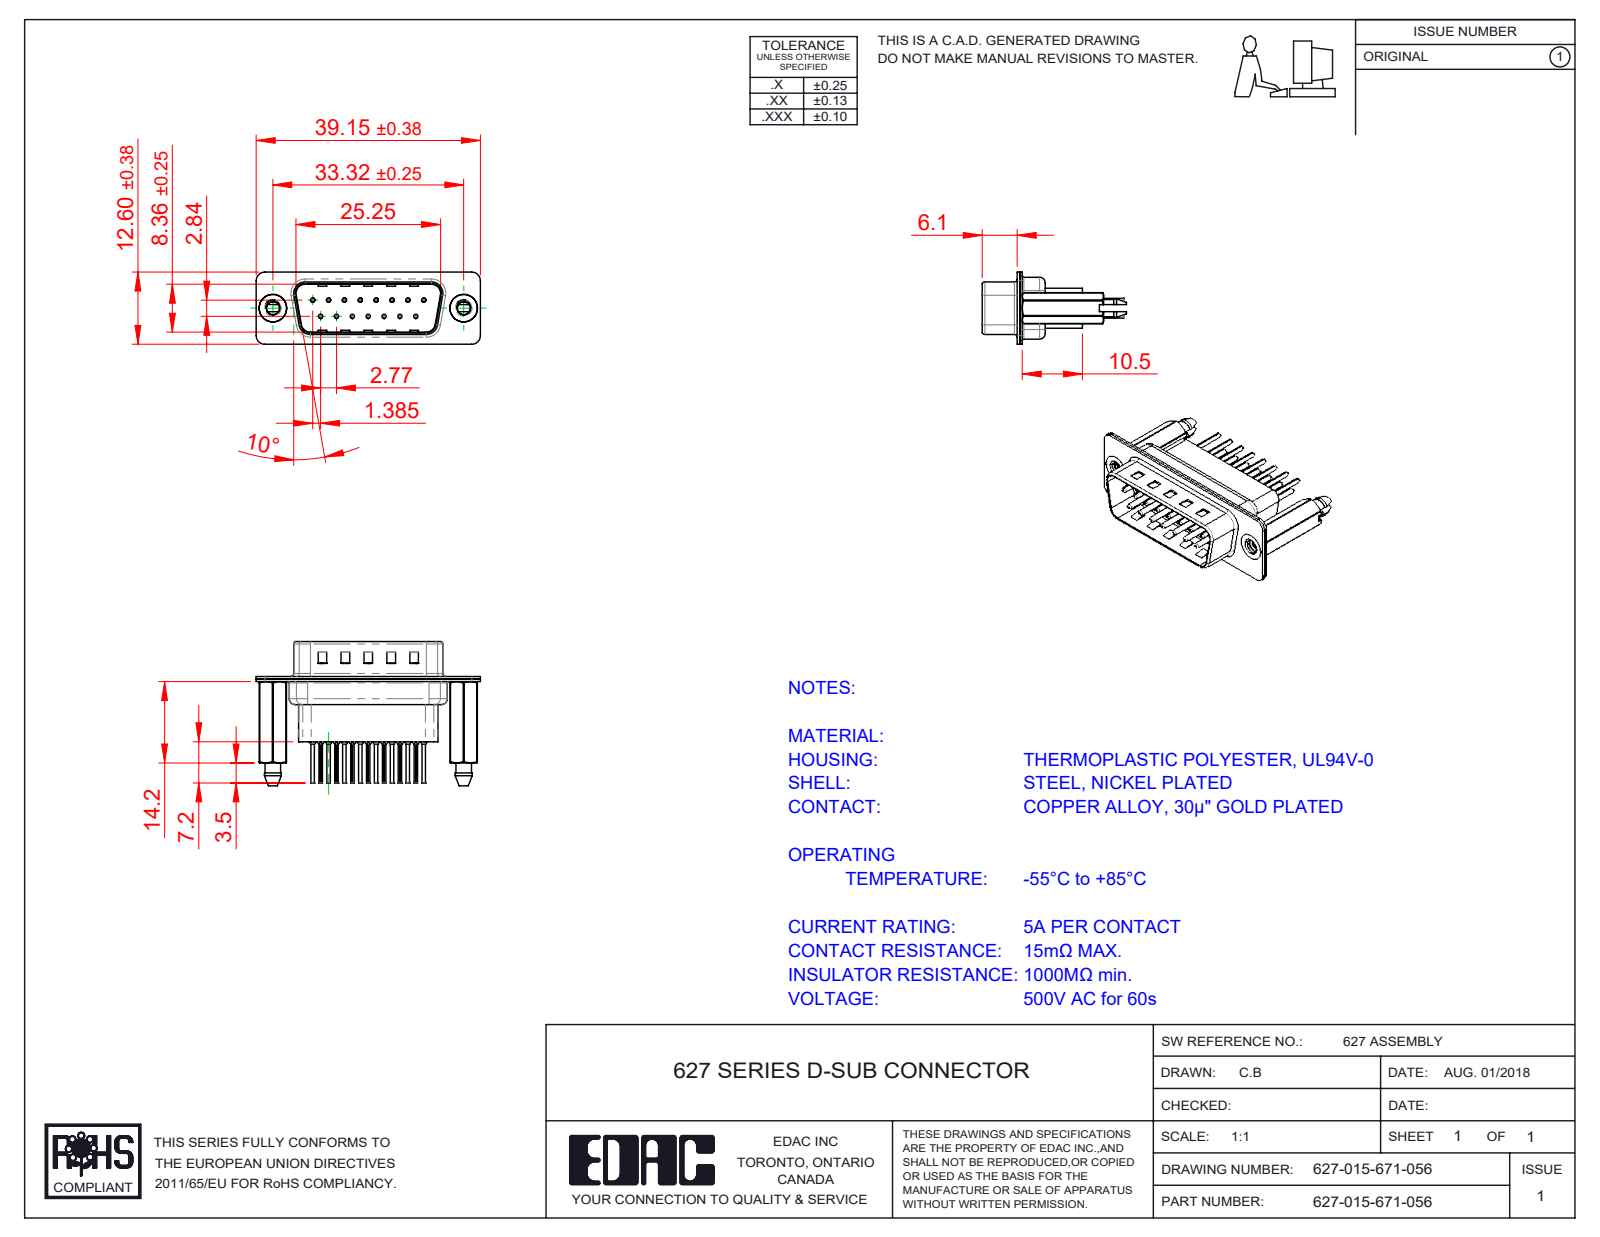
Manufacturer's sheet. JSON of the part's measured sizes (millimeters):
{"part_name": "627 Housing_15 HP; 627 Shell Rear_15 Contacts; 627 Contact Row 1_61; 627 Contact Row 2_61 (+3 more)", "step_written_by": "SolidWorks 2020 (CONFIG_CONTROL_DESIGN)", "units": "millimeters", "bodies": {"solids": 20, "faces": 1918, "planar": 531, "cylindrical": 754, "other": 633}, "overall_size": [39.15, 25.1, 12.6], "volume_mm3": 2911, "surface_area_mm2": 7517, "round_holes": [[0.2, 15], [0.35, 15], [1.1, 15], [1.6, 15], [2.26, 2], [4, 2], [4.8, 2]], "round_bosses_or_shafts": [[2, 15], [1.5, 15], [0.75, 15], [0.6, 15], [4.9, 2]], "partial_cylinders_radius": [[0.1, 30], [1.5, 18], [2, 12], [1.6, 10], [0.5, 8], [0.25, 4], [0.6, 4], [0.65, 4]], "face_to_face_distances": [0.4, 0.45, 0.9, 0.82, 9.58, 4.76, 1.5, 0.68, 7.68, 1.4], "hole_center_spacings": [3.16, 2.77, 5.54, 8.31, 11.08, 5.03, 5.04, 7.48]}
